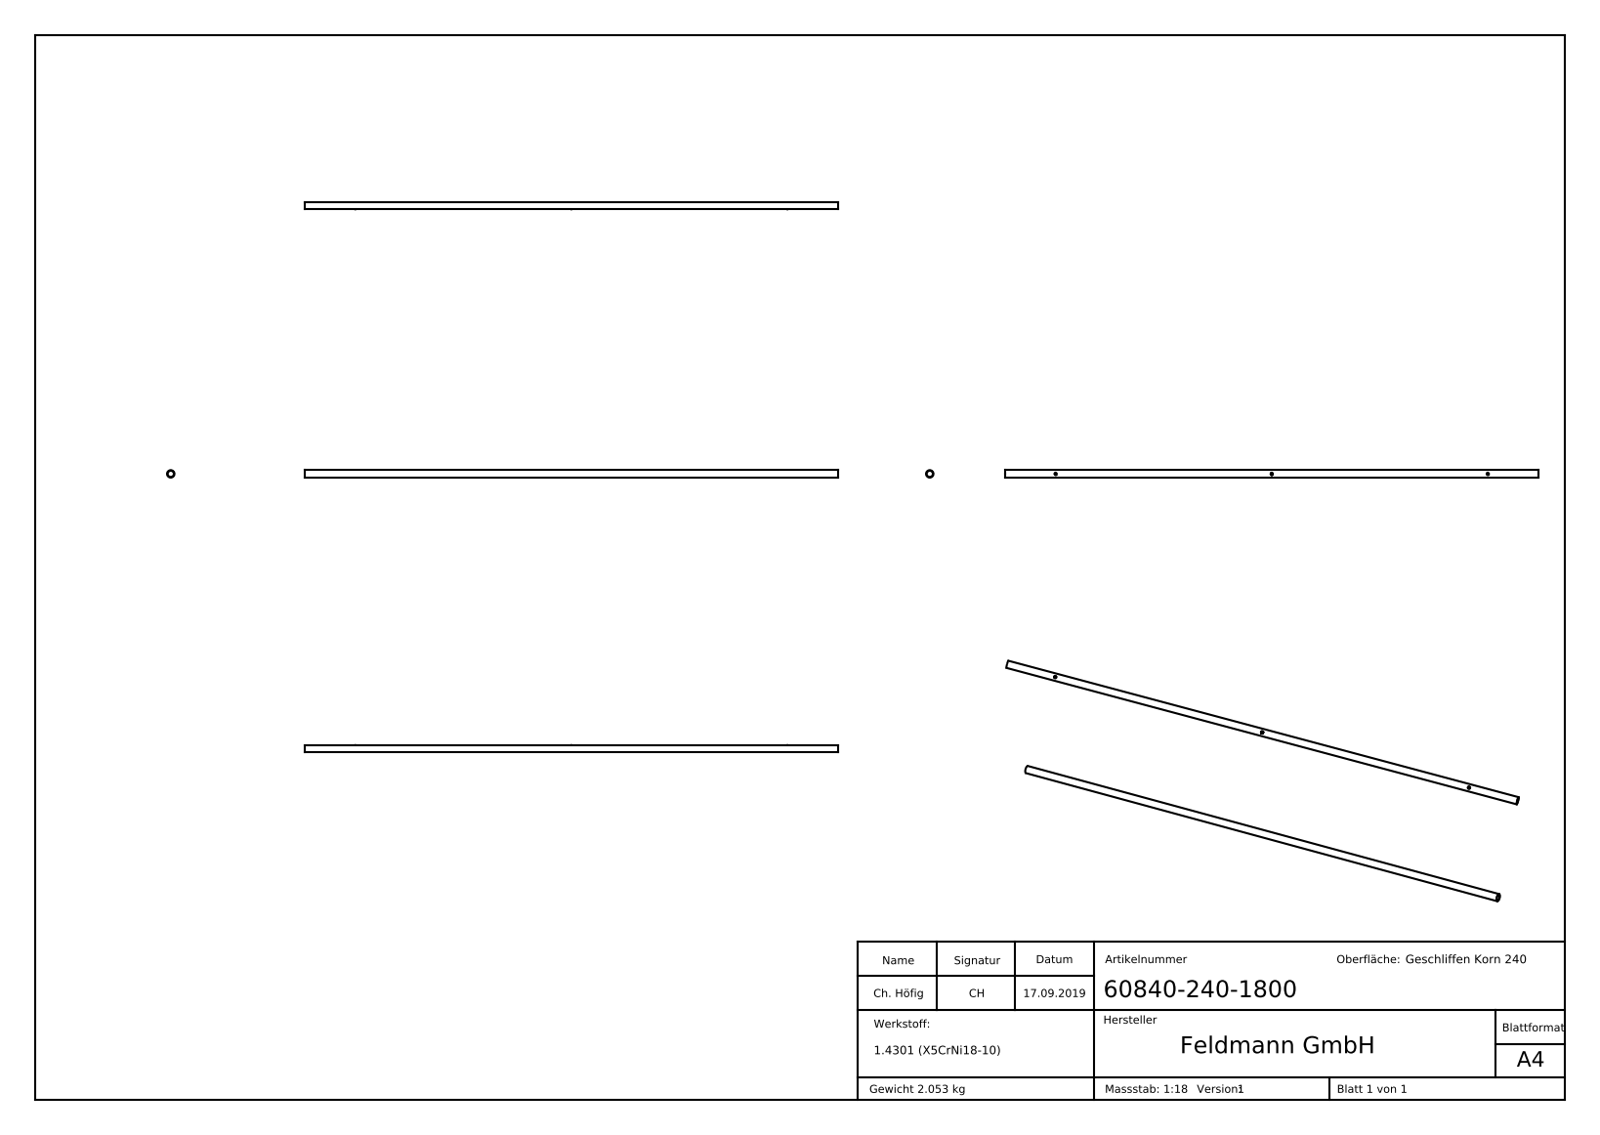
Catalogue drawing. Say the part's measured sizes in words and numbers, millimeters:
The part is named "60840-240-1800". Its 3-D file was written by "SolidWorks 2015 (CONFIG_CONTROL_DESIGN)". It is 1 solid with 303 faces: 105 planar, 56 cylindrical and 142 other. Overall it measures 1800 by 25 by 25 millimeters. Its volume is 259 903 cubic millimeters and its surface area 260 336 square millimeters. Round holes: 3 of diameter 6.8, 1 of diameter 21. Round bosses or shafts: 1 of diameter 25. Partial cylindrical surfaces (rounded edges, fillets, slot ends): 1 of radius 10.6. The main face-to-face distances are 1800, 0.39, 2.97, 3.66, 3.27, 7.38, 2.42, 6.09, 3.67, 3.09. The hole center spacings are 730, 1460.
